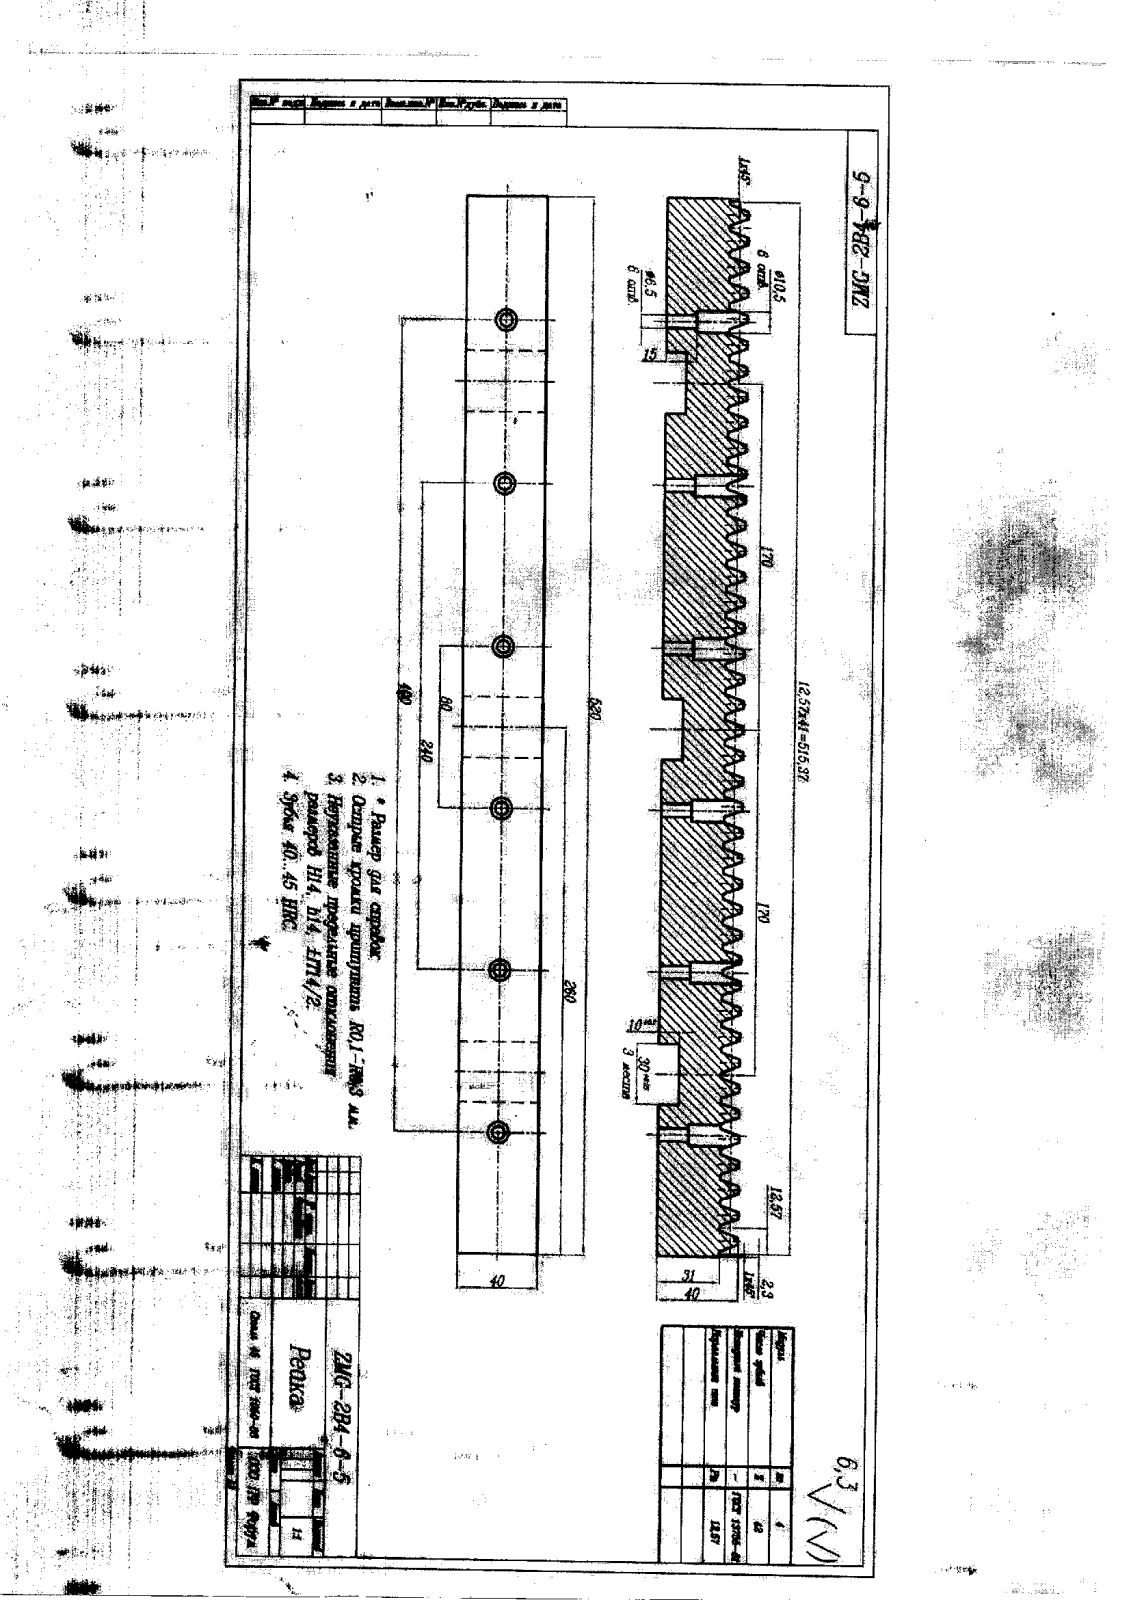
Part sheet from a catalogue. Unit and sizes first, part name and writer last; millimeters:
Units: millimetres
Overall size (bounding box): 1240 × 52.5 × 25
Round holes (diameter × count): ⌀8 ×2
Partial cylindrical surfaces — rounded edges, fillets, slot ends (radius × count): R2 ×96, R5 ×20, R2.5 ×12
Main face-to-face distances: 25, 11.34, 22.68, 34.02, 102.05, 113.39, 52.5, 45.36, 90.71, 79.37
Hole centre spacings: 1200
Volume: 1 167 000 mm³ · Surface area: 313 360 mm²
Bodies: 1 solid, 650 faces (518 planar, 130 cylindrical, 2 other)
Part name (STEP PRODUCT): Рейка
STEP written by: ASCON Math Kernel (CONFIG_CONTROL_DESIGN)
